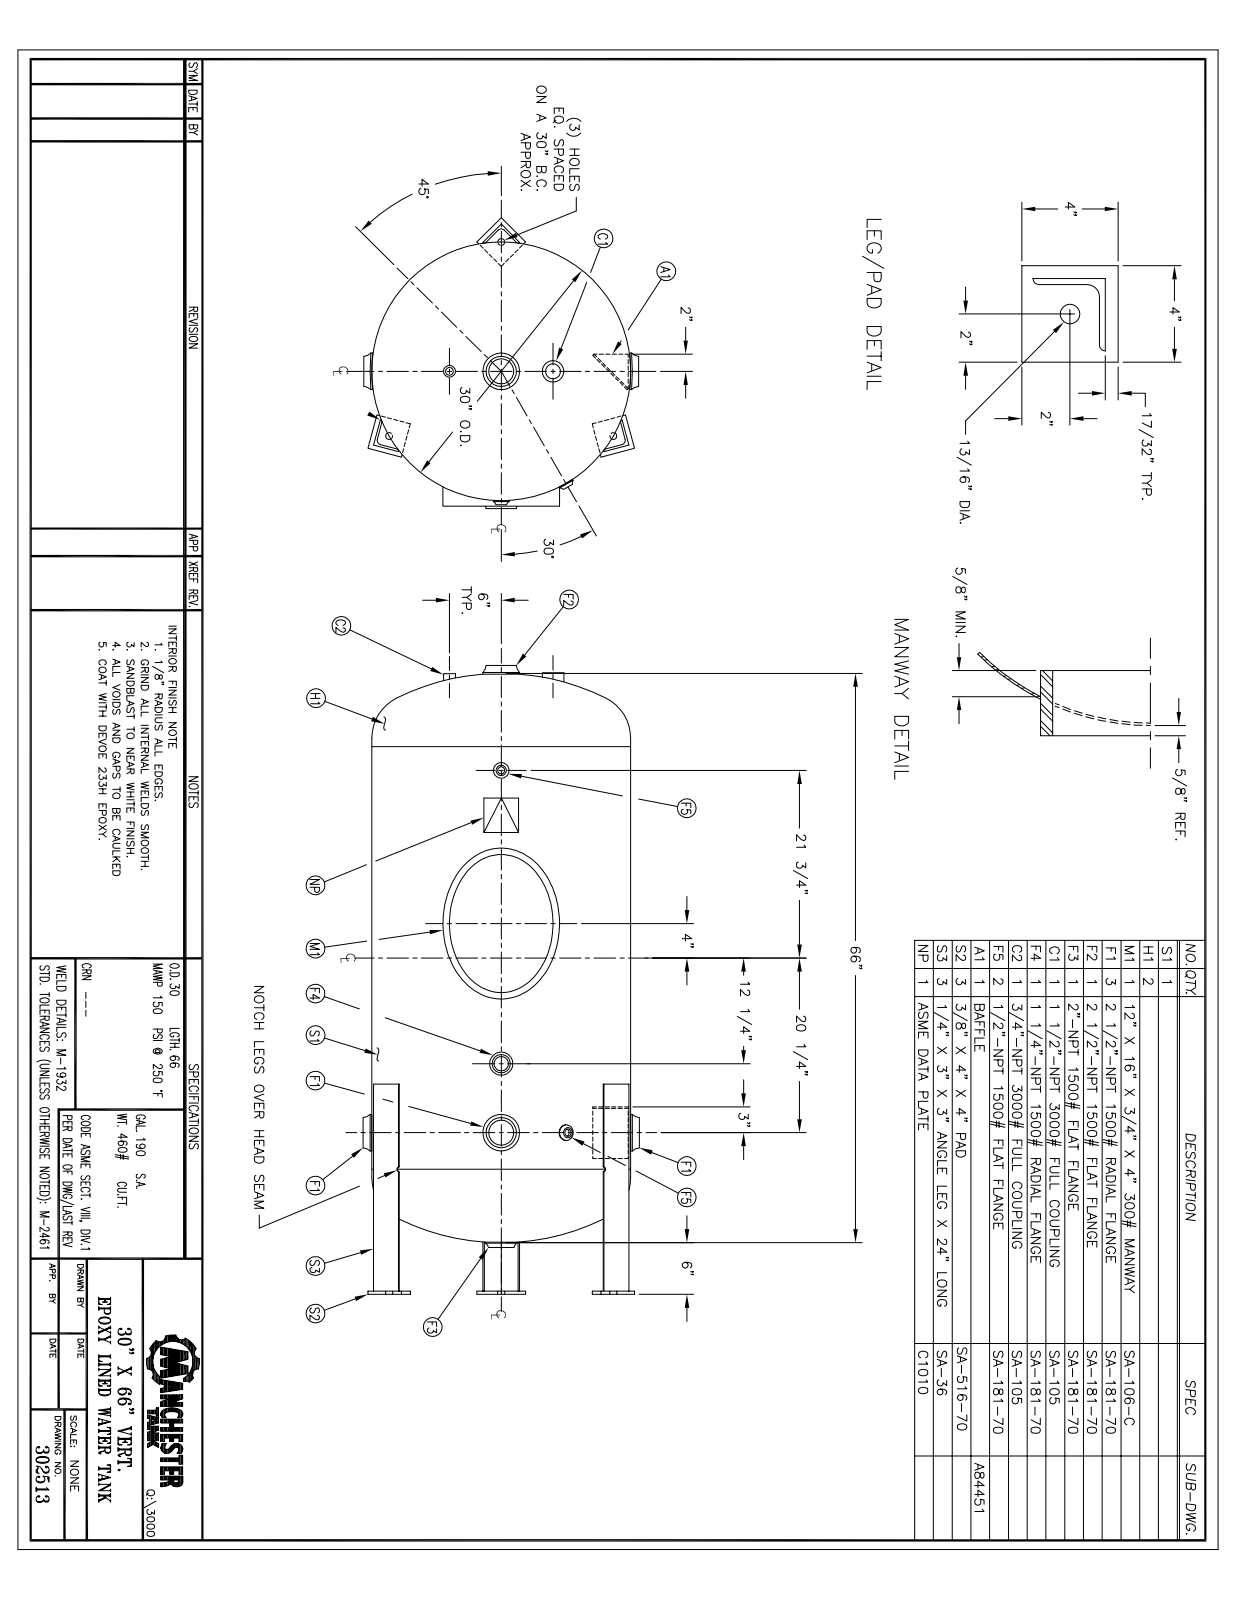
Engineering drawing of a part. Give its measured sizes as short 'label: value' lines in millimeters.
name: 302513
written by: SolidWorks 2011 (CONFIG_CONTROL_DESIGN)
unit: mm
bodies: 0 solids, 330 faces (128 planar, 105 cylindrical, 97 other)
size: 1849.4 × 986.2 × 813.1
holes: 3× ⌀20.7, 2× ⌀21.3, 2× ⌀73, 2× ⌀73, 1× ⌀26.7, 1× ⌀38.1, 1× ⌀42.2, 1× ⌀48.3, 1× ⌀60.3, 1× ⌀66.7, 1× ⌀752.6, 1× ⌀752.8
bosses: 2× ⌀108, 2× ⌀46.1, 2× ⌀25.4, 1× ⌀762, 1× ⌀752.6, 1× ⌀103.2, 1× ⌀88.9, 1× ⌀84.2
rounds: 12× R6.4, 4× R33.5, 3× R12, 3× R17.7, 2× R9.5, 1× R4.7, 1× R150.3, 1× R152.4
face distances: 5.7, 9.5, 76.2, 82.5, 87, 76.8, 81.3, 4.5, 188.5, 358.8
hole spacings: 381, 152.4, 260.4, 410.4, 518.6, 659.9, 203.2, 304.8
